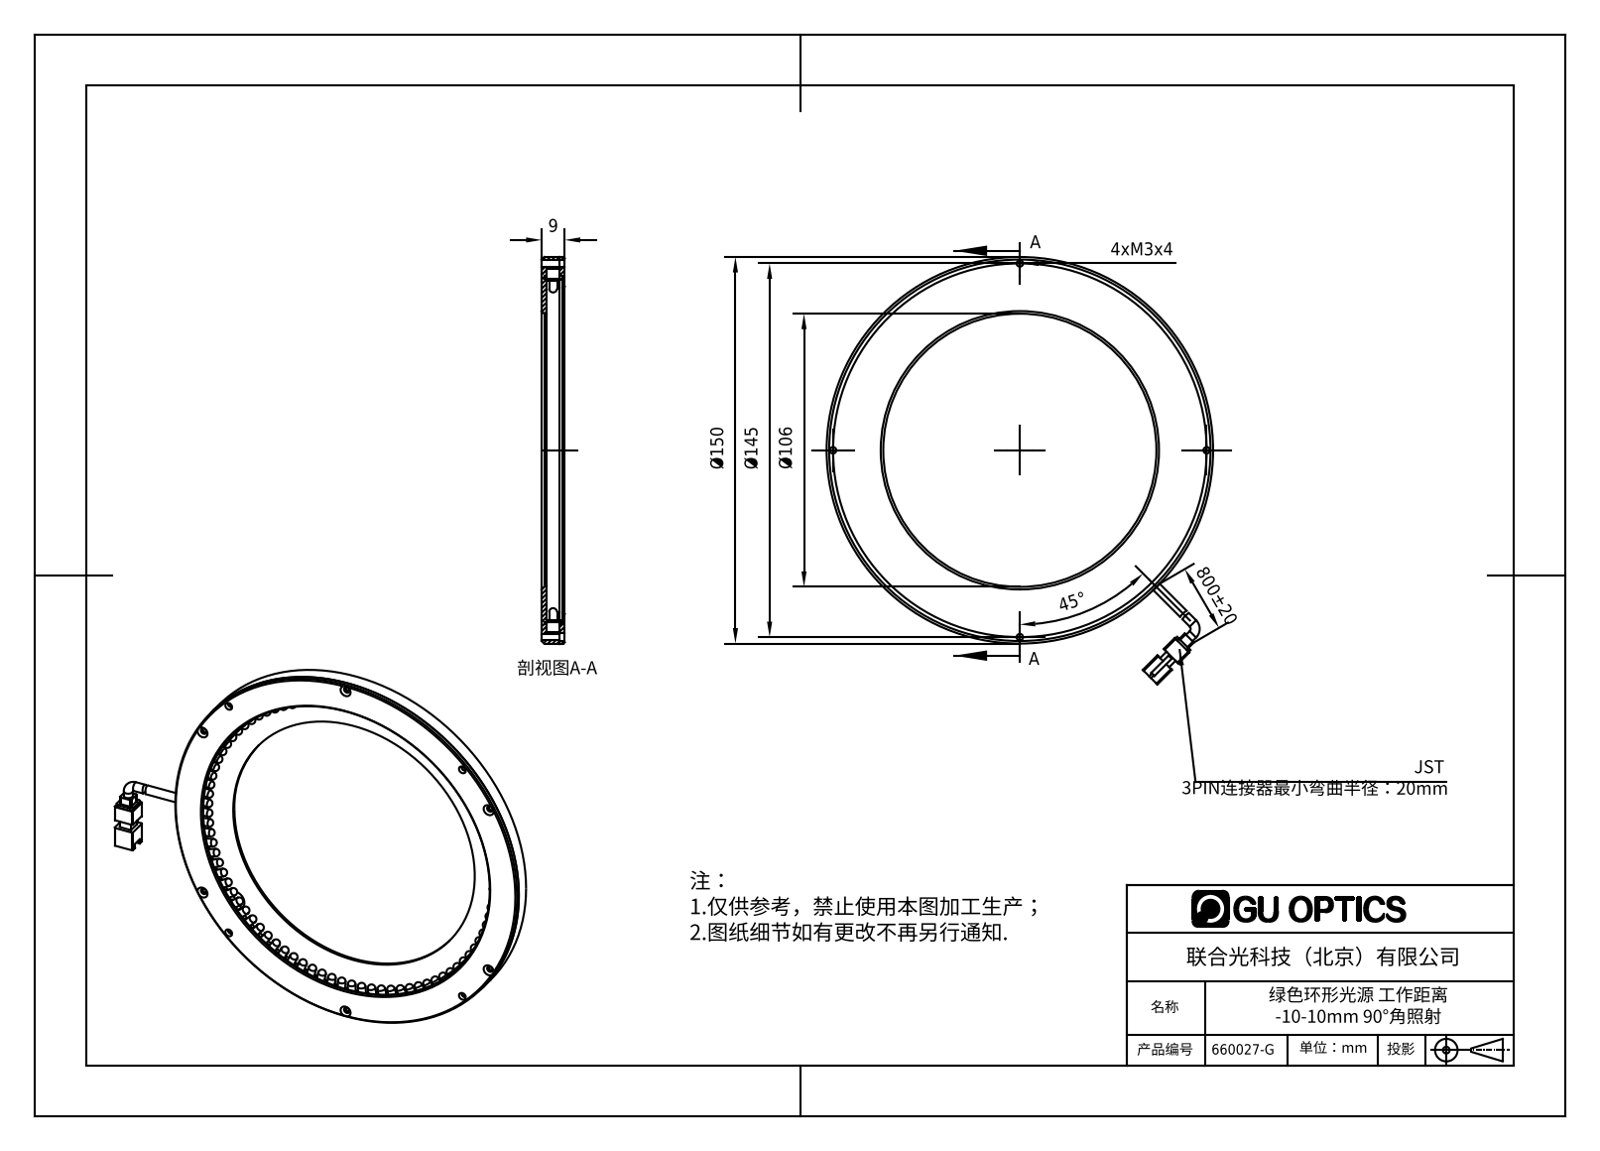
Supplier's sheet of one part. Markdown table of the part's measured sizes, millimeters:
| quantity | value |
| --- | --- |
| part name | 660027-G |
| STEP written by | SolidWorks 2016 (AUTOMOTIVE_DESIGN) |
| units | millimeters |
| bodies | 95 solids, 1781 faces (1163 planar, 492 cylindrical, 126 other) |
| overall size | 177 × 150 × 11 |
| volume | 41 228 mm³ |
| surface area | 51 986 mm² |
| round holes (diameter × count) | 1.6 × 6, 2 × 6, 2.4 × 6, 2.5 × 4, 3 × 4, 8 × 2, 3.5 × 1, 106 × 1, 126 × 1, 132 × 1, 135 × 1, 141 × 1 |
| round bosses / shafts (diameter × count) | 4 × 90, 3 × 90, 3.5 × 2, 150 × 1, 134 × 1, 133 × 1 |
| partial cylindrical surfaces (radius × count) | 0.5 × 8, 1 × 4, 2 × 2, 3.5 × 2 |
| main face-to-face distances | 2, 7, 5, 1, 9, 8, 6, 0.5, 1.5, 3.77 |
| hole center spacings | 72.5, 72.49, 145, 88.27, 102.53, 115.03, 125.57, 133.96 |
